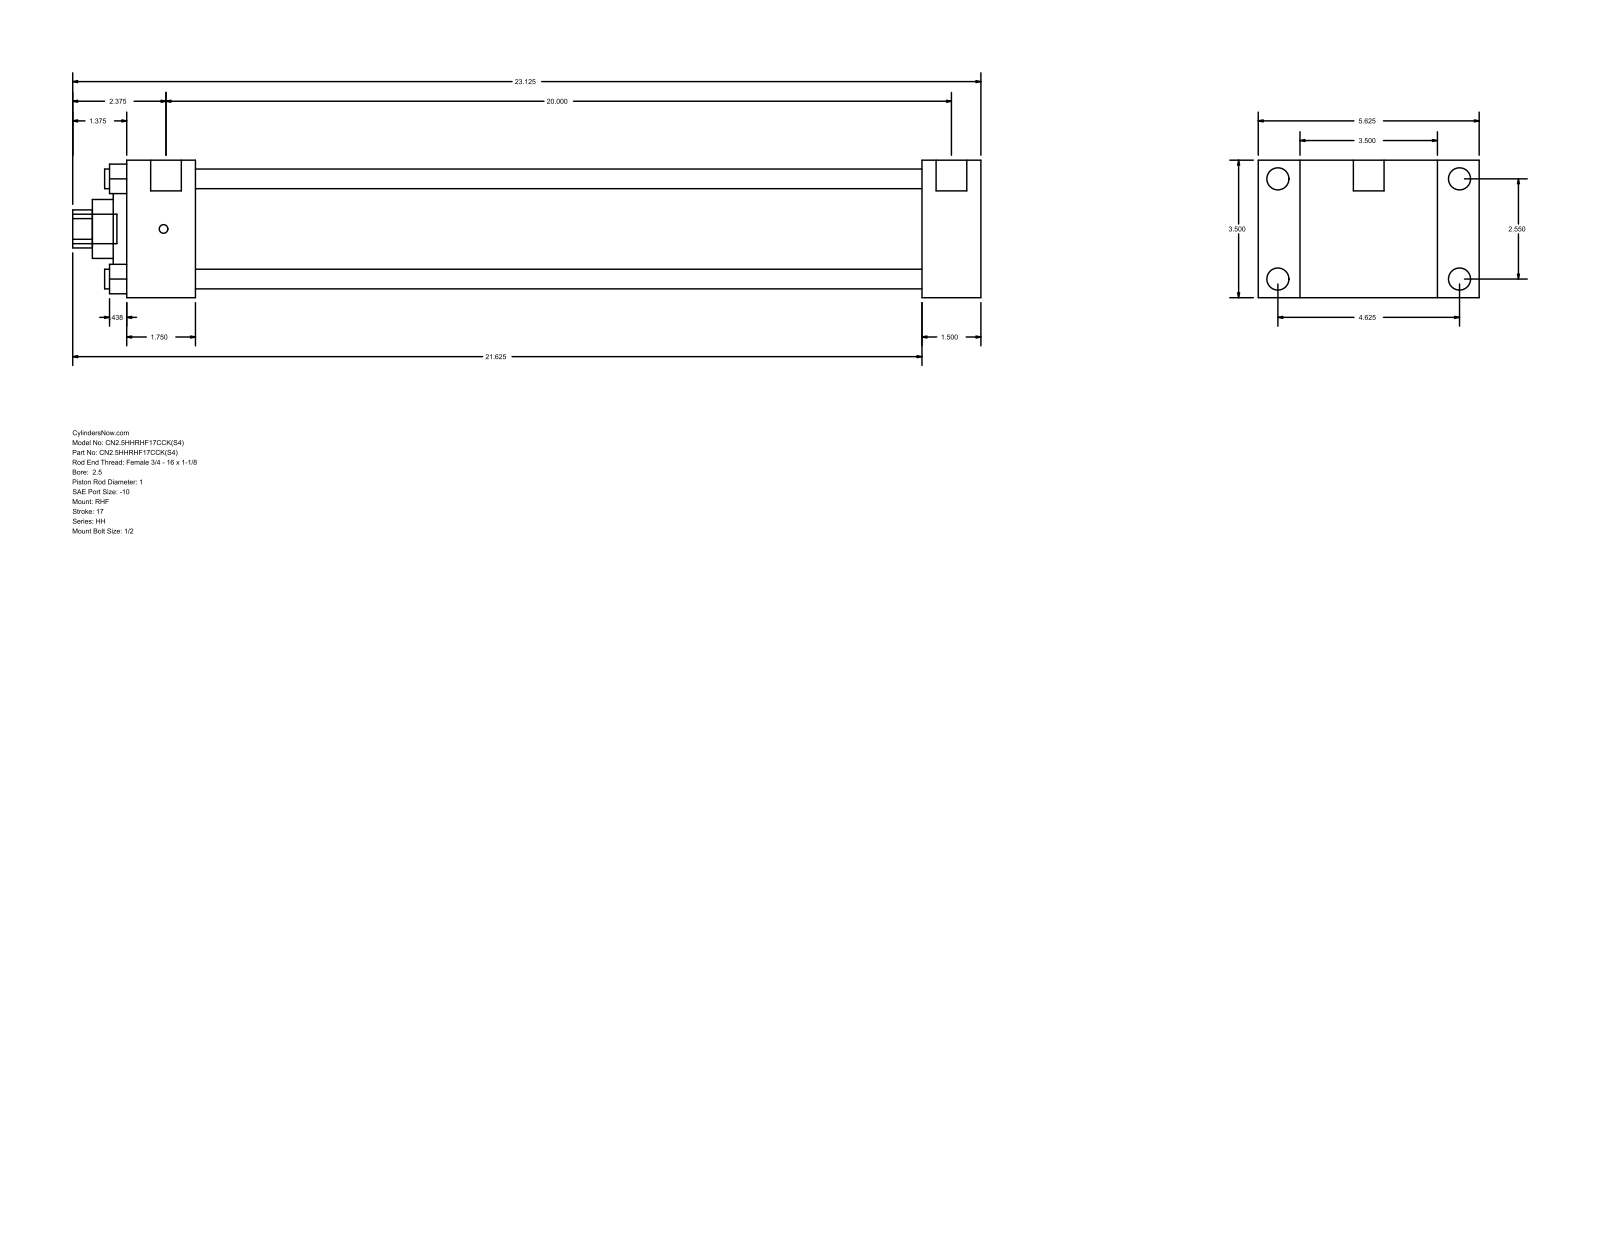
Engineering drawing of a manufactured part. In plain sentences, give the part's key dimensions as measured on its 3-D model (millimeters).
The part is named "HH_RHF__0250_1". Its 3-D file was written by "GSSL Pune (CONFIG_CONTROL_DESIGN)". It is 0 solids with 90 faces: 61 planar, 29 cylindrical and 0 other. Overall it measures 587.38 by 142.88 by 88.9 millimeters. Round holes: 4 of diameter 12.7, 1 of diameter 25.4, 1 of diameter 38.1, 1 of diameter 60.33, 1 of diameter 73.03. Round bosses or shafts: 4 of diameter 14.3, 4 of diameter 5.56, 2 of diameter 19.84, 1 of diameter 19.05. Partial cylindrical surfaces (rounded edges, fillets, slot ends): 1 of radius 12.29. The main face-to-face distances are 88.9, 38.11, 26.99, 115.89, 514.35, 552.46, 142.88, 44.46, 469.89, 508. The hole center spacings are 45.79, 64.76, 91.58.
